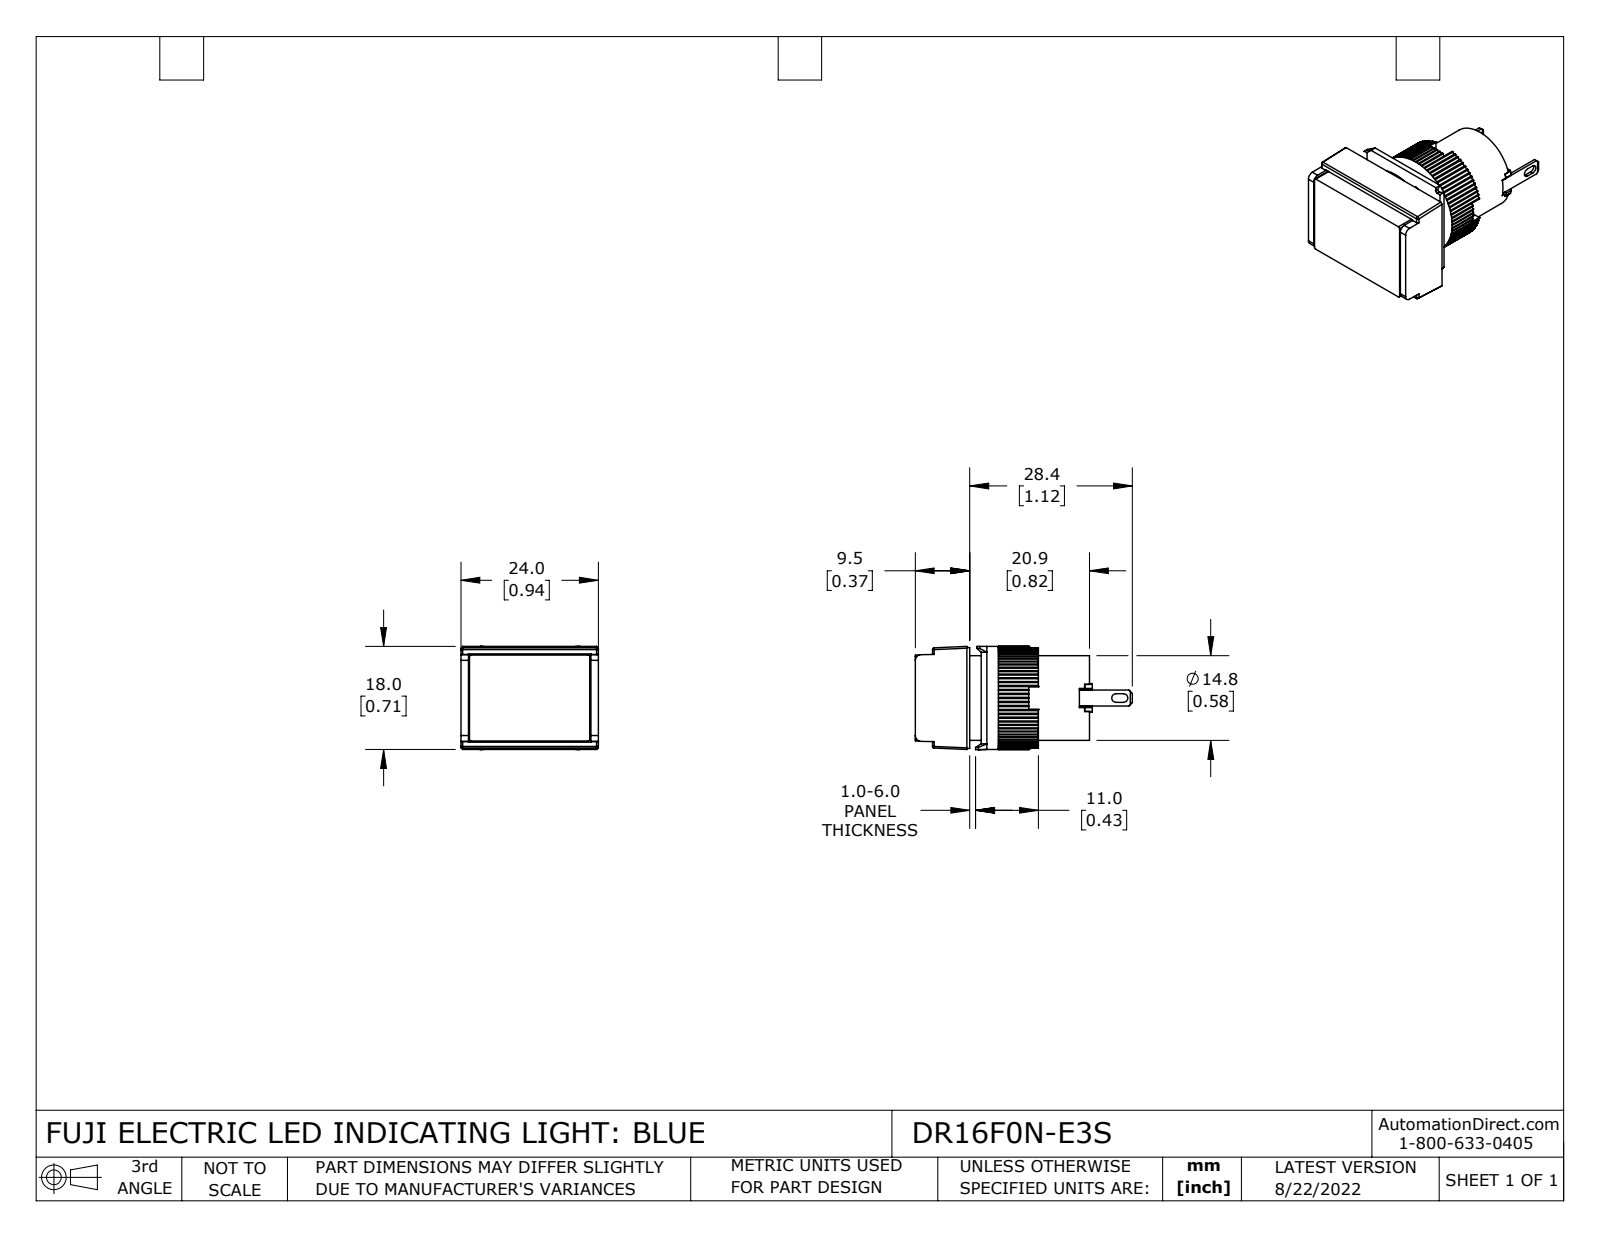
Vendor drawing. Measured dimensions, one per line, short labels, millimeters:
name: DR16F0N-E3S
written by: SolidWorks 2021 (CONFIG_CONTROL_DESIGN)
unit: mm
bodies: 10 solids, 501 faces (322 planar, 175 cylindrical, 4 other)
size: 37.9 × 24 × 18
volume: 7 340 mm³; area: 5 777 mm²
holes: 1× ⌀13.8, 1× ⌀14.8
bosses: 1× ⌀18, 1× ⌀17.6
rounds: 80× R0.3, 8× R0.2, 6× R0.3, 2× R0.8, 2× R1
face distances: 5.4, 9, 3.6, 8.9, 12.5, 3.5, 21.4, 17.9, 11.5, 1.5
